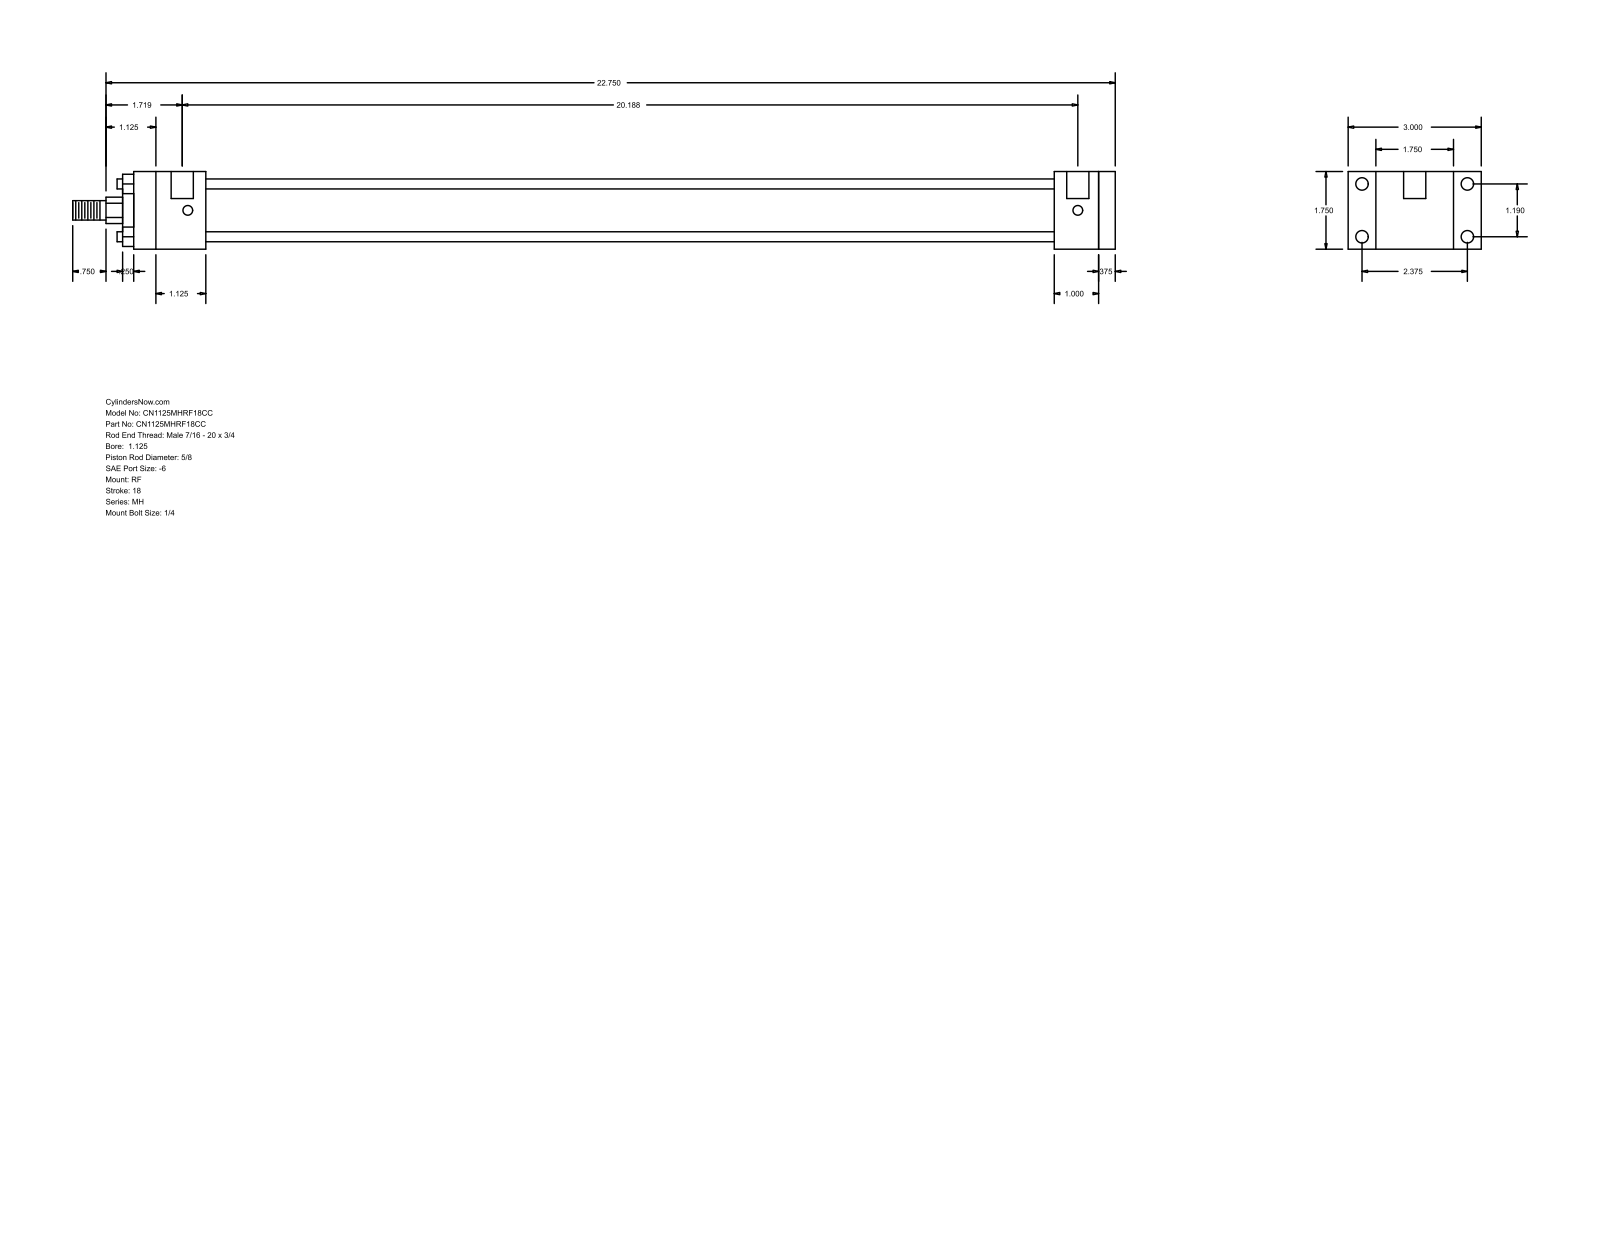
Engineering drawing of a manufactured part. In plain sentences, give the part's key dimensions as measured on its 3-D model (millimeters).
The part is named "MH_RF__0112_0.625". Its 3-D file was written by "GSSL Pune (CONFIG_CONTROL_DESIGN)". It is 0 solids with 92 faces: 64 planar, 28 cylindrical and 0 other. Overall it measures 596.9 by 76.2 by 44.45 millimeters. Round holes: 4 of diameter 5.56, 4 of diameter 7.14, 2 of diameter 12.7. Round bosses or shafts: 4 of diameter 5.71, 1 of diameter 34.92, 1 of diameter 28.57, 1 of diameter 15.88, 1 of diameter 11.11. Partial cylindrical surfaces (rounded edges, fillets, slot ends): 1 of radius 7.54. The main face-to-face distances are 44.46, 9.52, 34.93, 561.97, 15.87, 511.18, 520.7, 485.77, 25.41, 41.27. The hole center spacings are 30.22, 60.32, 67.47, 509.59, 3.17, 512.76.
